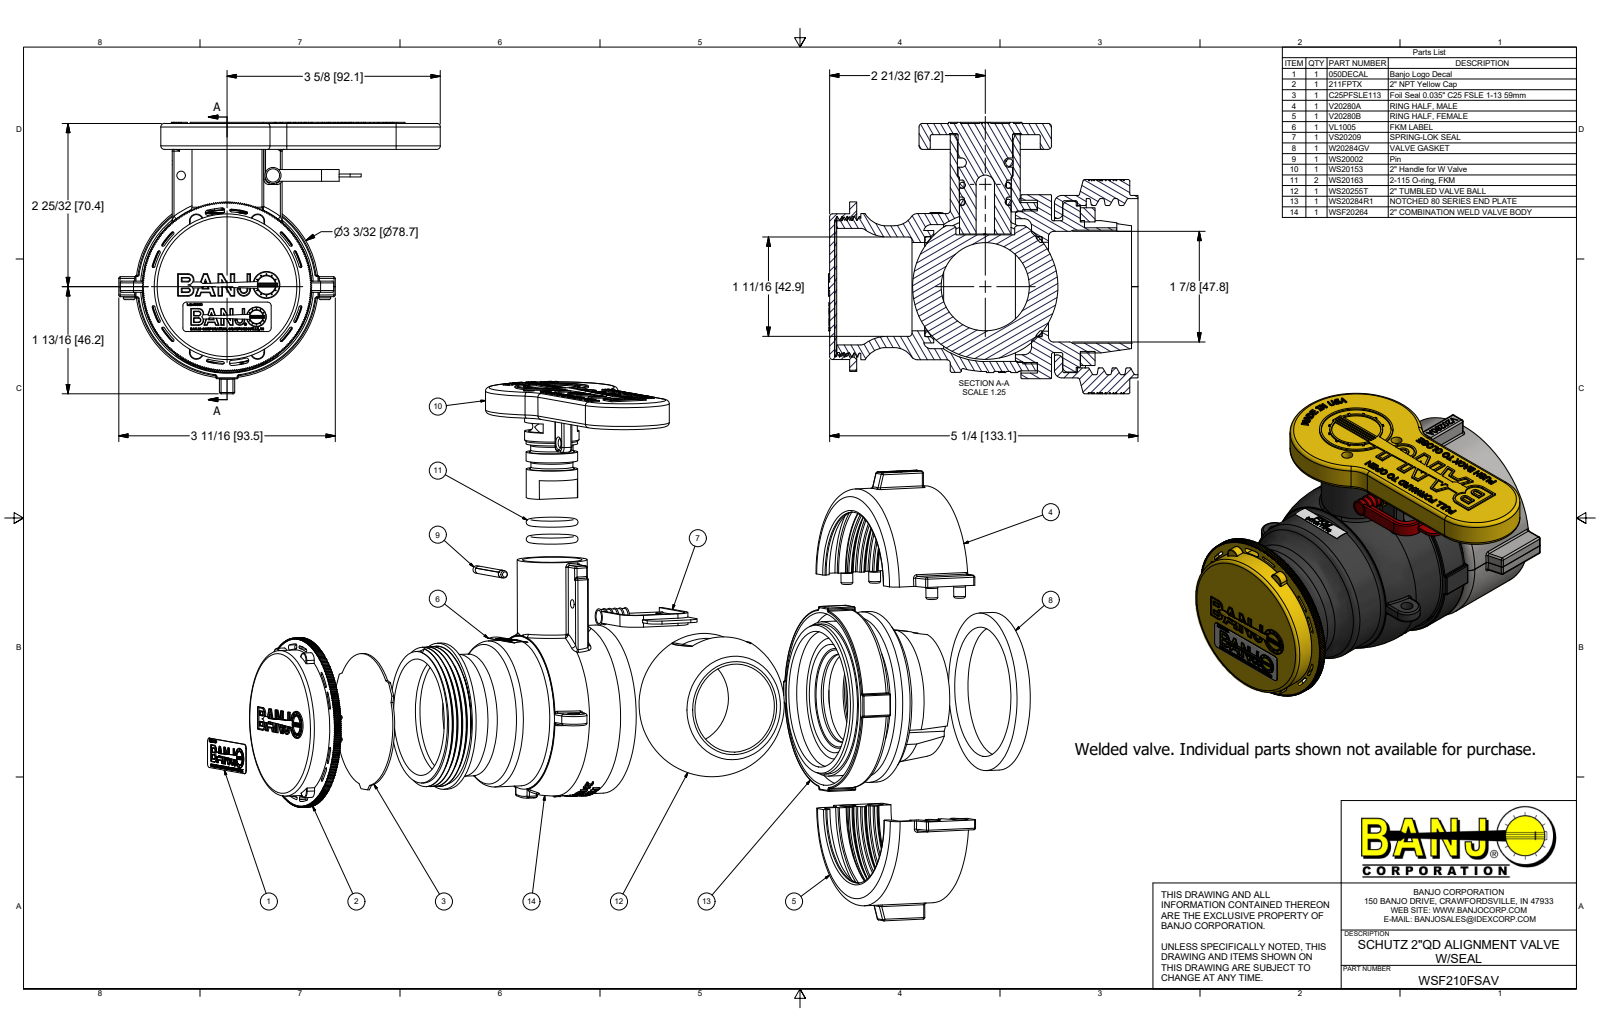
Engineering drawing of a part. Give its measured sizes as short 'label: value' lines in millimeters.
name: WSF210FSAV; VS20209; 211FPTX; 050DECAL (+8 more)
written by: Autodesk Inventor 2018 (AUTOMOTIVE_DESIGN)
unit: mm
bodies: 17 solids, 4820 faces (2534 planar, 1007 cylindrical, 1279 other)
size: 138.8 × 133.7 × 117.2
volume: 330 200 mm³; area: 171 500 mm²
holes: 4× ⌀5.3, 4× ⌀6.5, 2× ⌀3.7, 2× ⌀4.8, 2× ⌀5.3, 2× ⌀38.1, 1× ⌀4, 1× ⌀5.8, 1× ⌀7.8, 1× ⌀7.9, 1× ⌀8.2, 1× ⌀11.1
bosses: 4× ⌀5.1, 2× ⌀57.2, 1× ⌀78.7, 1× ⌀77.5, 1× ⌀74.2, 1× ⌀73.7, 1× ⌀73.2, 1× ⌀72.6
rounds: 78× R0.8, 32× R0.4, 4× R1.5, 4× R1.6, 4× R3, 4× R6.4, 3× R1.8, 3× R5.7
face distances: 3, 4.8, 2.2, 0.9, 0.9, 2.2, 105.2, 106.1, 106.1, 108.3
hole spacings: 13.3, 41.5, 51.9, 56.7, 63.3, 70, 73.8, 84.4
